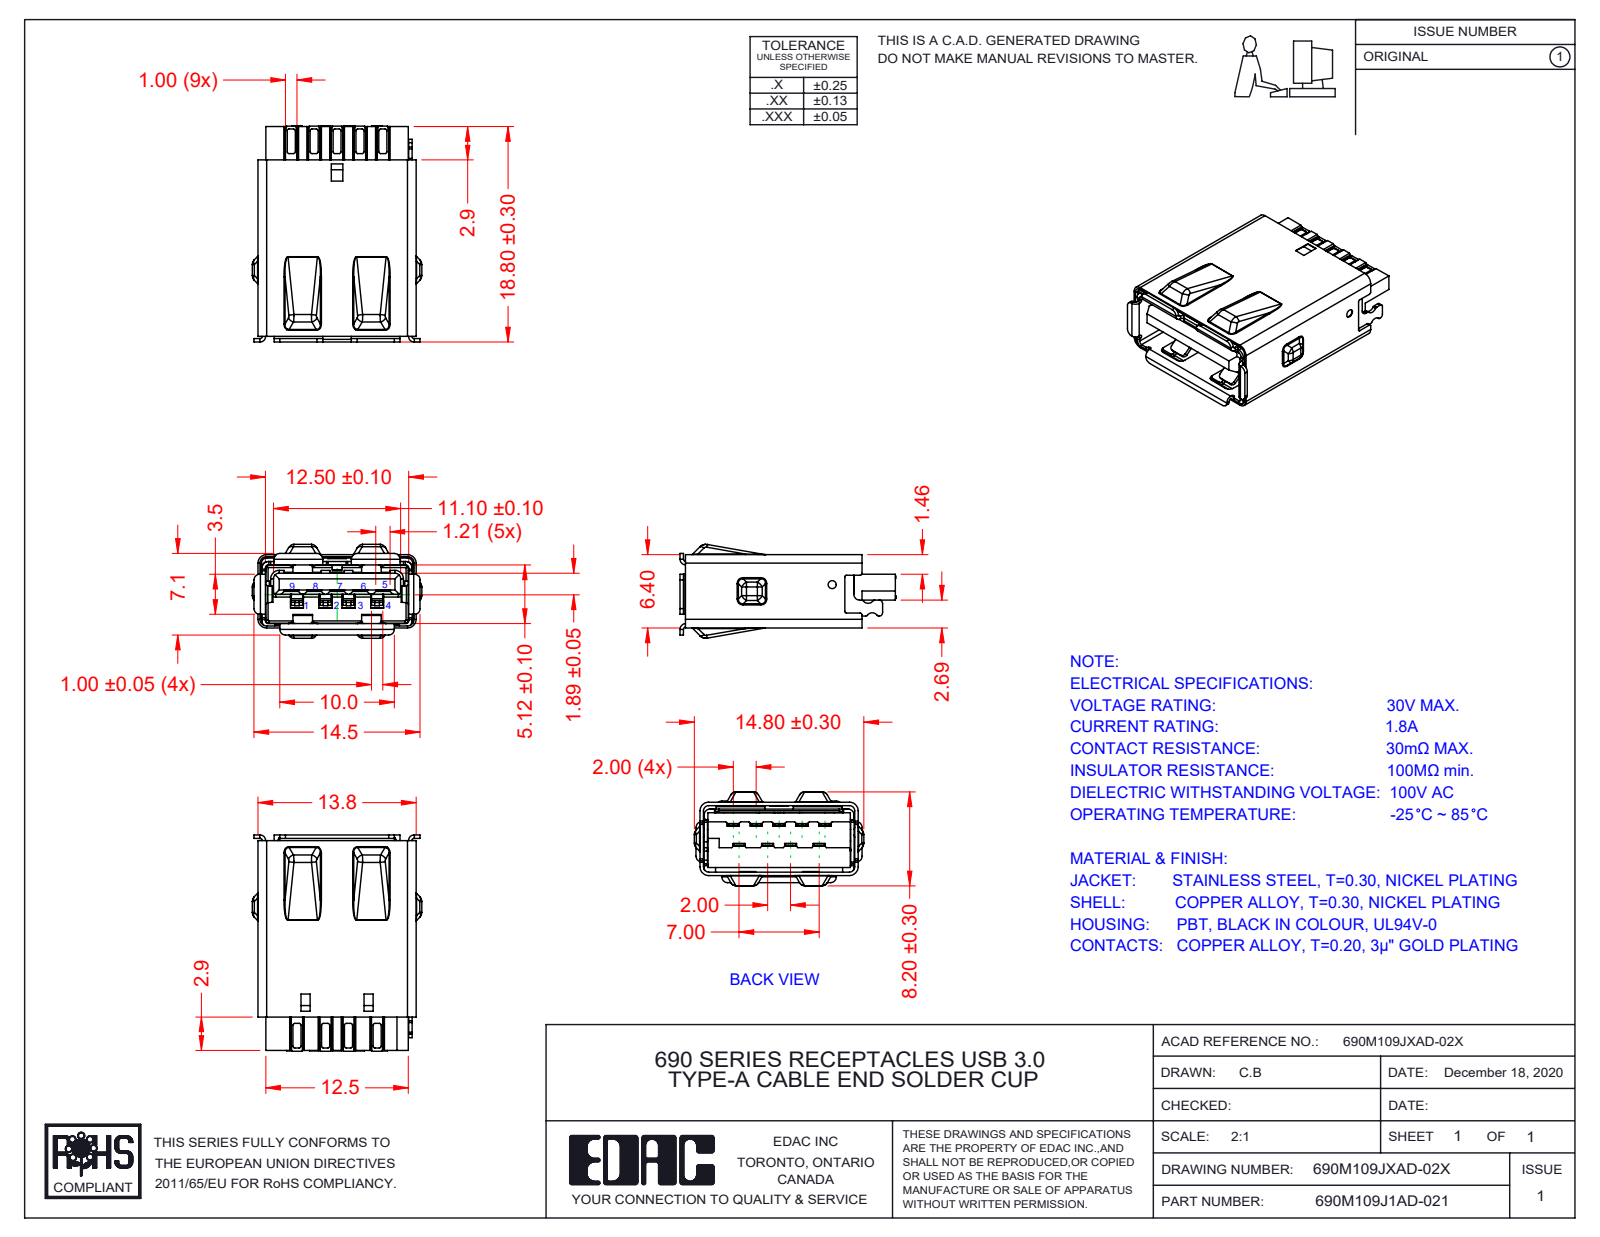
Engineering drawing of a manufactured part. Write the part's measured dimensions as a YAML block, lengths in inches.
part_name: "Contact2 690M109JXAD-02X; Contact1 690M109JXAD-02X; Contact3 690M109JXAD-02X; Insulator2 690M109JXAD-02X_Black (+6 more)"
step_written_by: "SolidWorks 2020 (AUTOMOTIVE_DESIGN)"
units: inches
bodies: {solids: 13, faces: 2416, planar: 1451, cylindrical: 775, other: 190}
overall_size: [0.743, 0.583, 0.323]
volume: 0.049
surface_area: 6.172
round_holes:
  - {diameter: 0.028, count: 1}
partial_cylinders:
  - {radius: 0.006, count: 140}
  - {radius: 0.008, count: 68}
  - {radius: 0.004, count: 58}
  - {radius: 0.02, count: 42}
  - {radius: 0.012, count: 32}
  - {radius: 0.005, count: 30}
  - {radius: 0.01, count: 20}
  - {radius: 0.024, count: 19}
face_to_face_distances: [0.217, 0.228, 0.24, 0.024, 0.014, 0.213, 0.225, 0.237, 0.518, 0.015]
